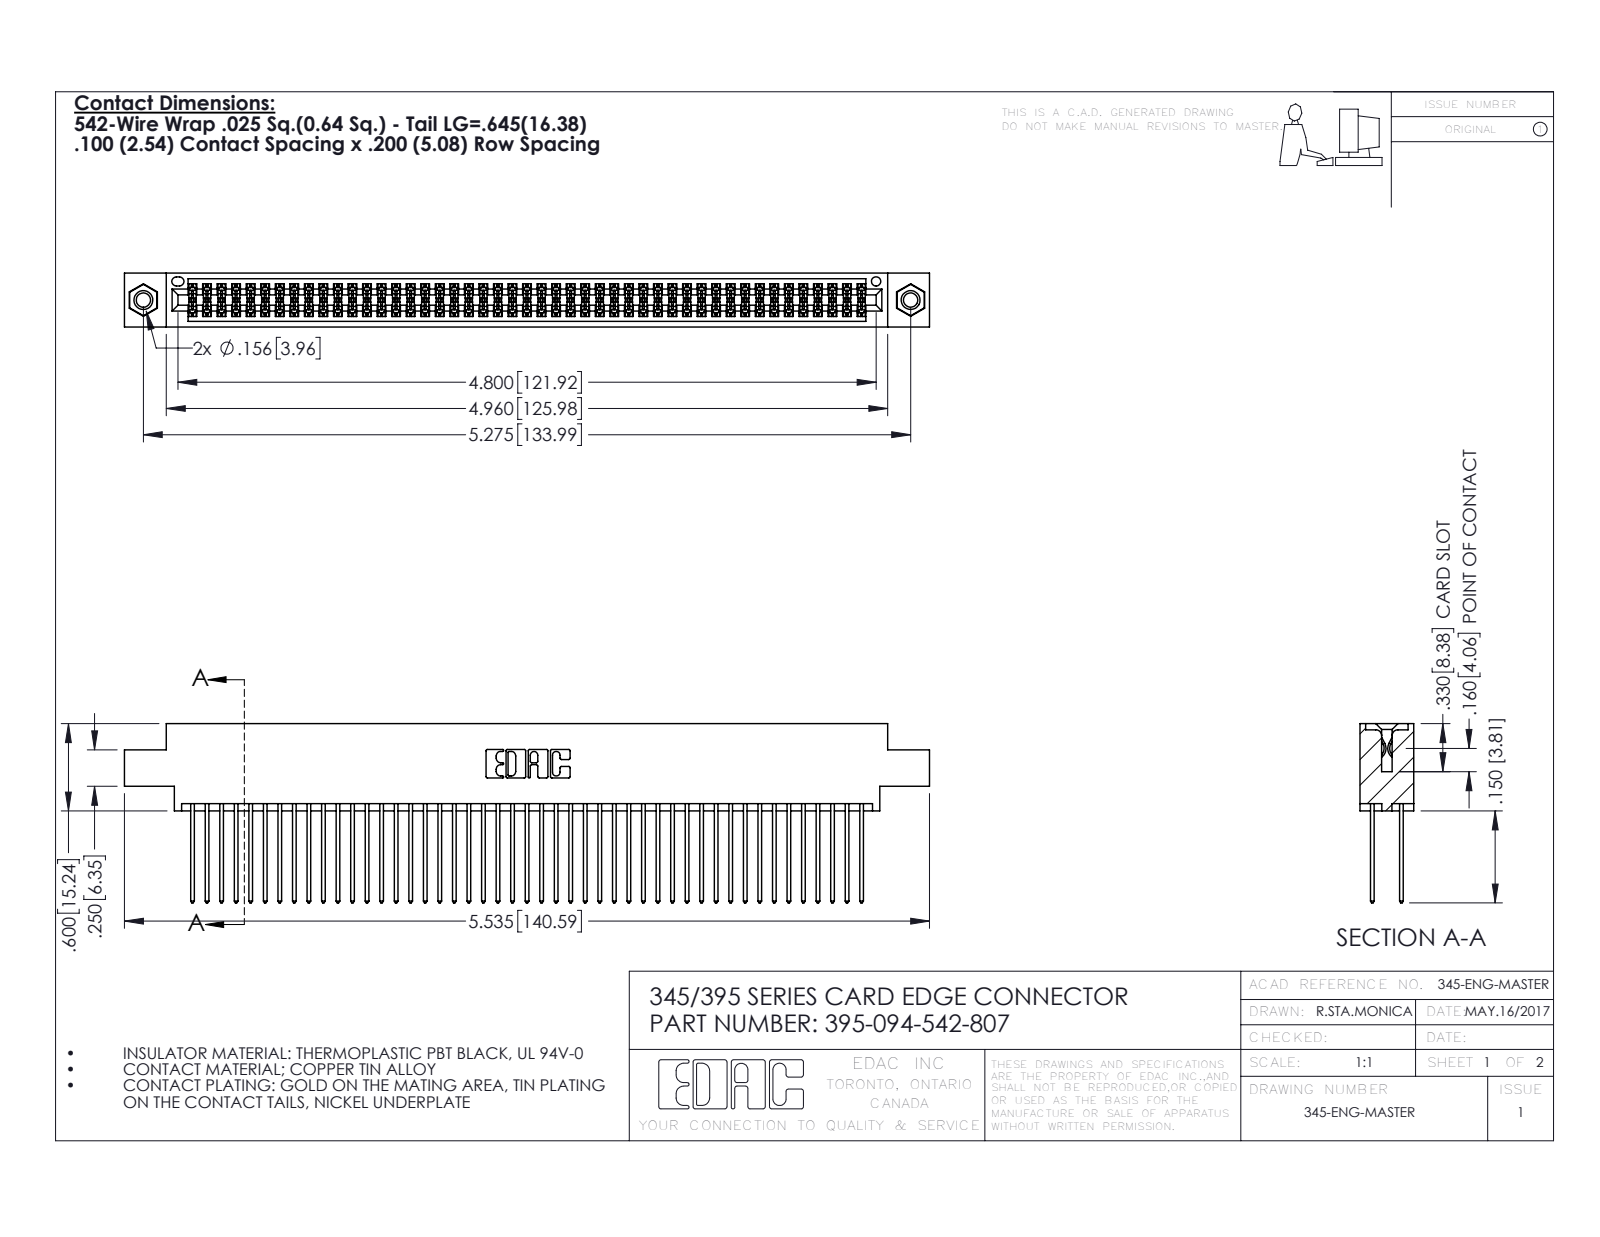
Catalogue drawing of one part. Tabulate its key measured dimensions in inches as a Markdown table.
| quantity | value |
| --- | --- |
| part name | 345 Part_0.170 Offset - 0.156 Dia-TI; 345-250-001_345-250-005-103; 395-094-542-807; 345-292-001_345-293-142 |
| STEP written by | SolidWorks 2016 (CONFIG_CONTROL_DESIGN) |
| units | inches |
| bodies | 97 solids, 4890 faces (3218 planar, 1656 cylindrical, 16 other) |
| overall size | 5.535 × 1.232 × 0.37 |
| volume | 0.855 in³ |
| surface area | 35.7 in² |
| round holes (diameter × count) | 0.098 × 2, 0.125 × 2, 0.156 × 2, 0.064 × 1 |
| round bosses / shafts (diameter × count) | 0.155 × 2 |
| partial cylindrical surfaces (radius × count) | 0.006 × 141, 0.01 × 94, 0.01 × 22, 0.007 × 6, 0.031 × 6, 0.026 × 3, 0.014 × 2, 0.019 × 2 |
| main face-to-face distances | 0.072, 0.298, 0.2, 0.098, 0.272, 0.025, 0.37, 0.225, 0.175, 0.149 |
| hole center spacings | 0.27, 5.039, 5.275 |
